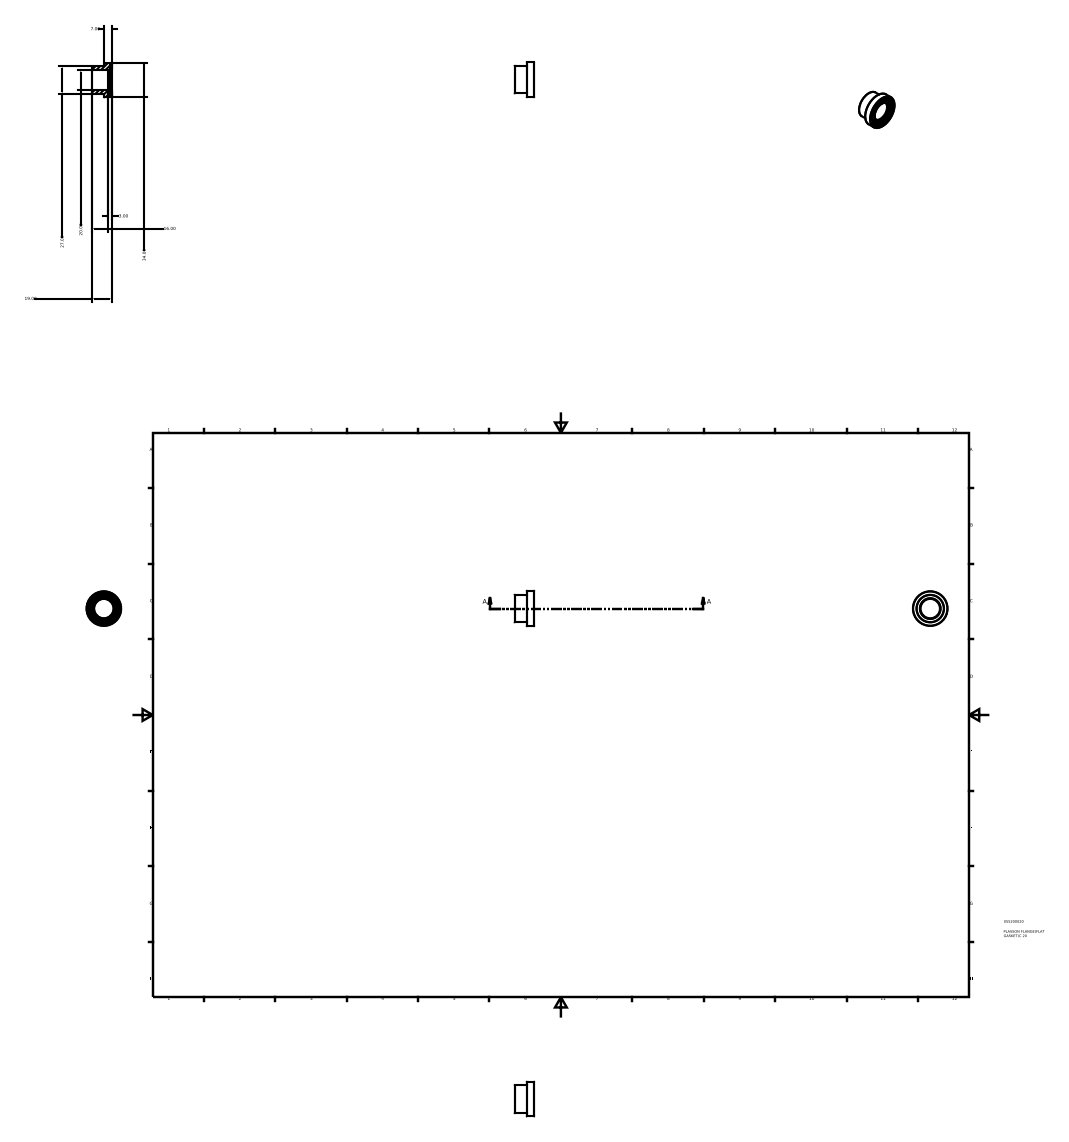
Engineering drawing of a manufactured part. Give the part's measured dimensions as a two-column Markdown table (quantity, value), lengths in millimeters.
| quantity | value |
| --- | --- |
| part name | 055200020 |
| STEP written by | Autodesk Inventor 2015 (AUTOMOTIVE_DESIGN) |
| units | millimeters |
| bodies | 1 solid, 33 faces (9 planar, 9 cylindrical, 15 other) |
| overall size | 34 × 34 × 19 |
| volume | 7 033 mm³ |
| surface area | 4 466 mm² |
| round holes (diameter × count) | 19 × 1, 20 × 1, 21.5 × 1, 26.5 × 1, 31.5 × 1 |
| round bosses / shafts (diameter × count) | 34 × 1, 29 × 1, 27 × 1, 24 × 1 |
| main face-to-face distances | 12, 19, 7, 17.95, 5.95, 1.05, 16, 4, 1.95, 3 |
